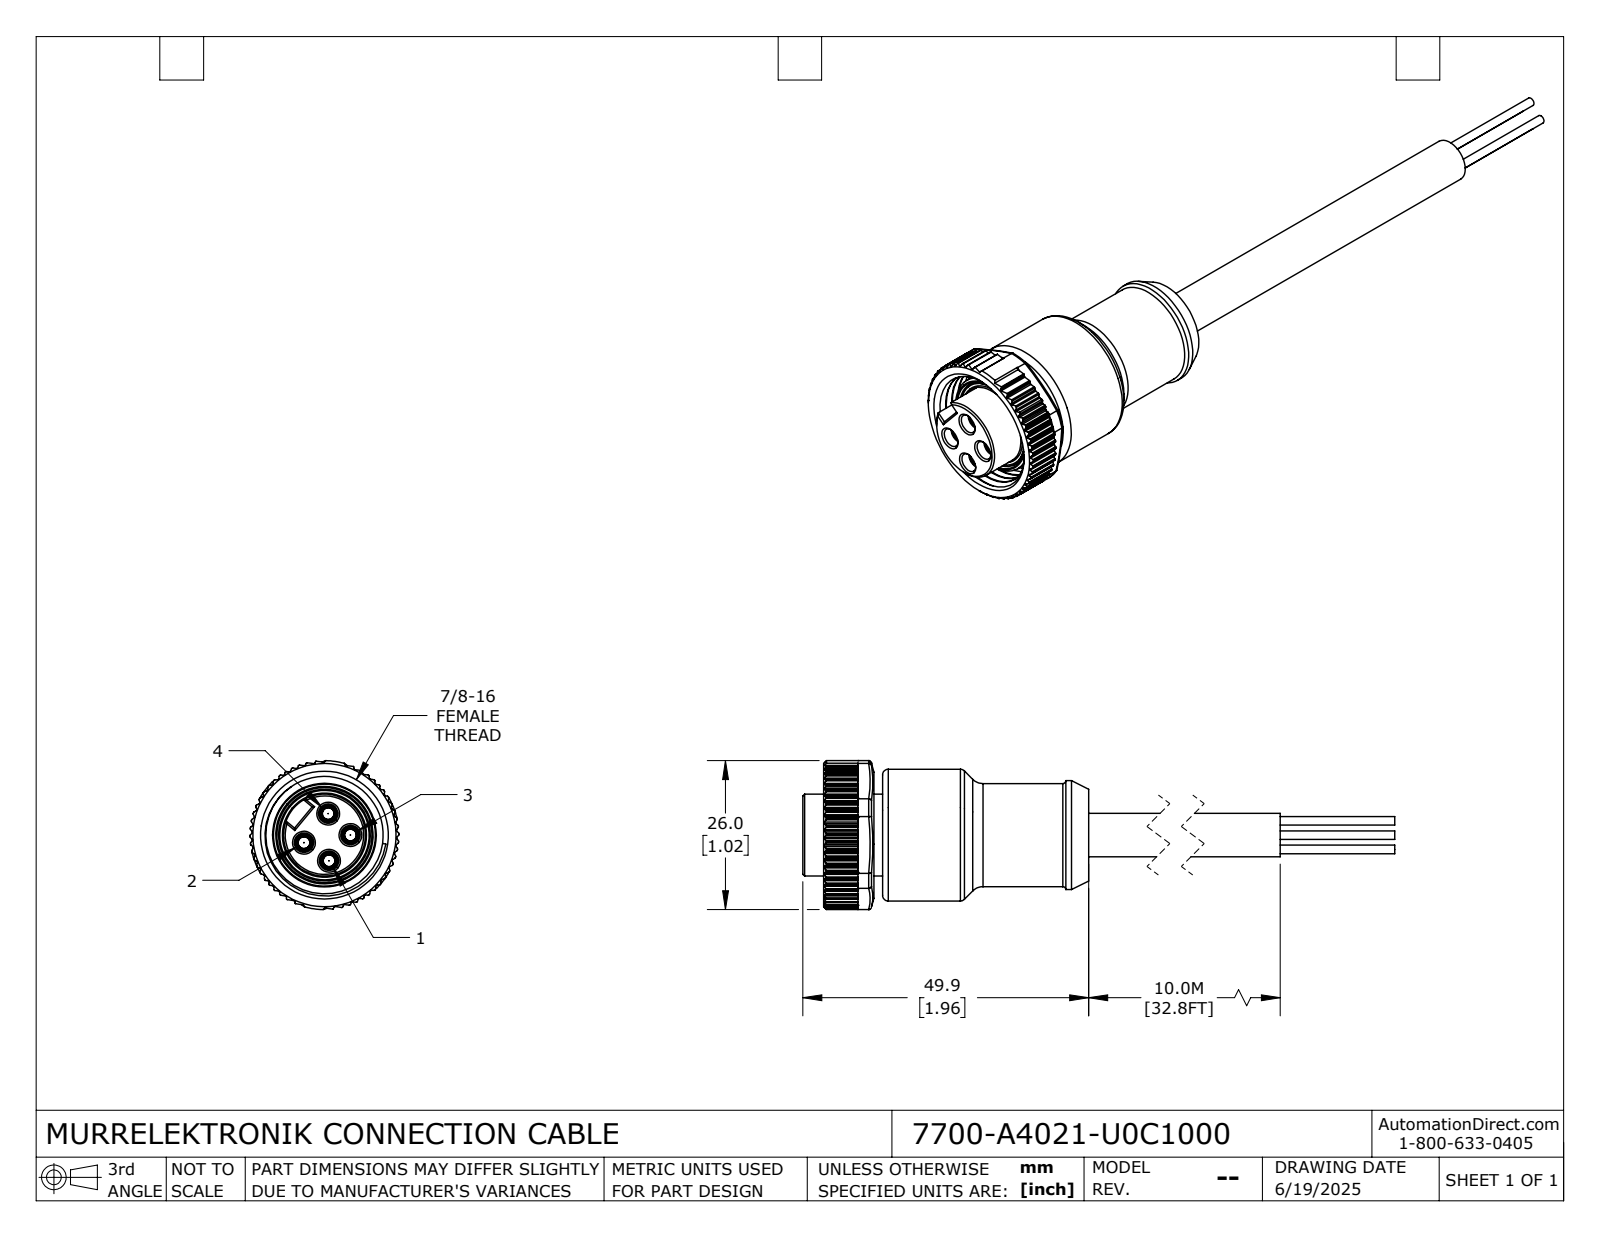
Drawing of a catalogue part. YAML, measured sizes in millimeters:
part_name: "7700-A4021-U0C1000"
step_written_by: "SolidWorks 2024 (CONFIG_CONTROL_DESIGN)"
units: millimeters
bodies: {solids: 1, faces: 674, planar: 296, cylindrical: 293, other: 85}
overall_size: [139.9, 26, 26]
volume: 18784
surface_area: 8325
round_holes:
  - {diameter: 2.05, count: 4}
  - {diameter: 3, count: 4}
  - {diameter: 3.4, count: 4}
  - {diameter: 15.5, count: 1}
  - {diameter: 15.6, count: 1}
  - {diameter: 20.5, count: 1}
  - {diameter: 22.23, count: 1}
round_bosses_or_shafts:
  - {diameter: 1.5, count: 4}
  - {diameter: 23, count: 1}
  - {diameter: 19, count: 1}
  - {diameter: 18.1, count: 1}
  - {diameter: 18, count: 1}
  - {diameter: 17.8, count: 1}
  - {diameter: 14.3, count: 1}
  - {diameter: 7.6, count: 1}
partial_cylinders:
  - {radius: 0.2, count: 126}
  - {radius: 0.3, count: 16}
  - {radius: 0.1, count: 4}
  - {radius: 0.73, count: 4}
  - {radius: 13, count: 1}
face_to_face_distances: [1.5, 37.5, 36, 3.6, 8.8, 10.3, 46.3, 12.4, 13.9, 49.9]
hole_center_spacings: [3.81, 4.54, 8.22, 5.39, 5.4, 5.84, 6.6]
